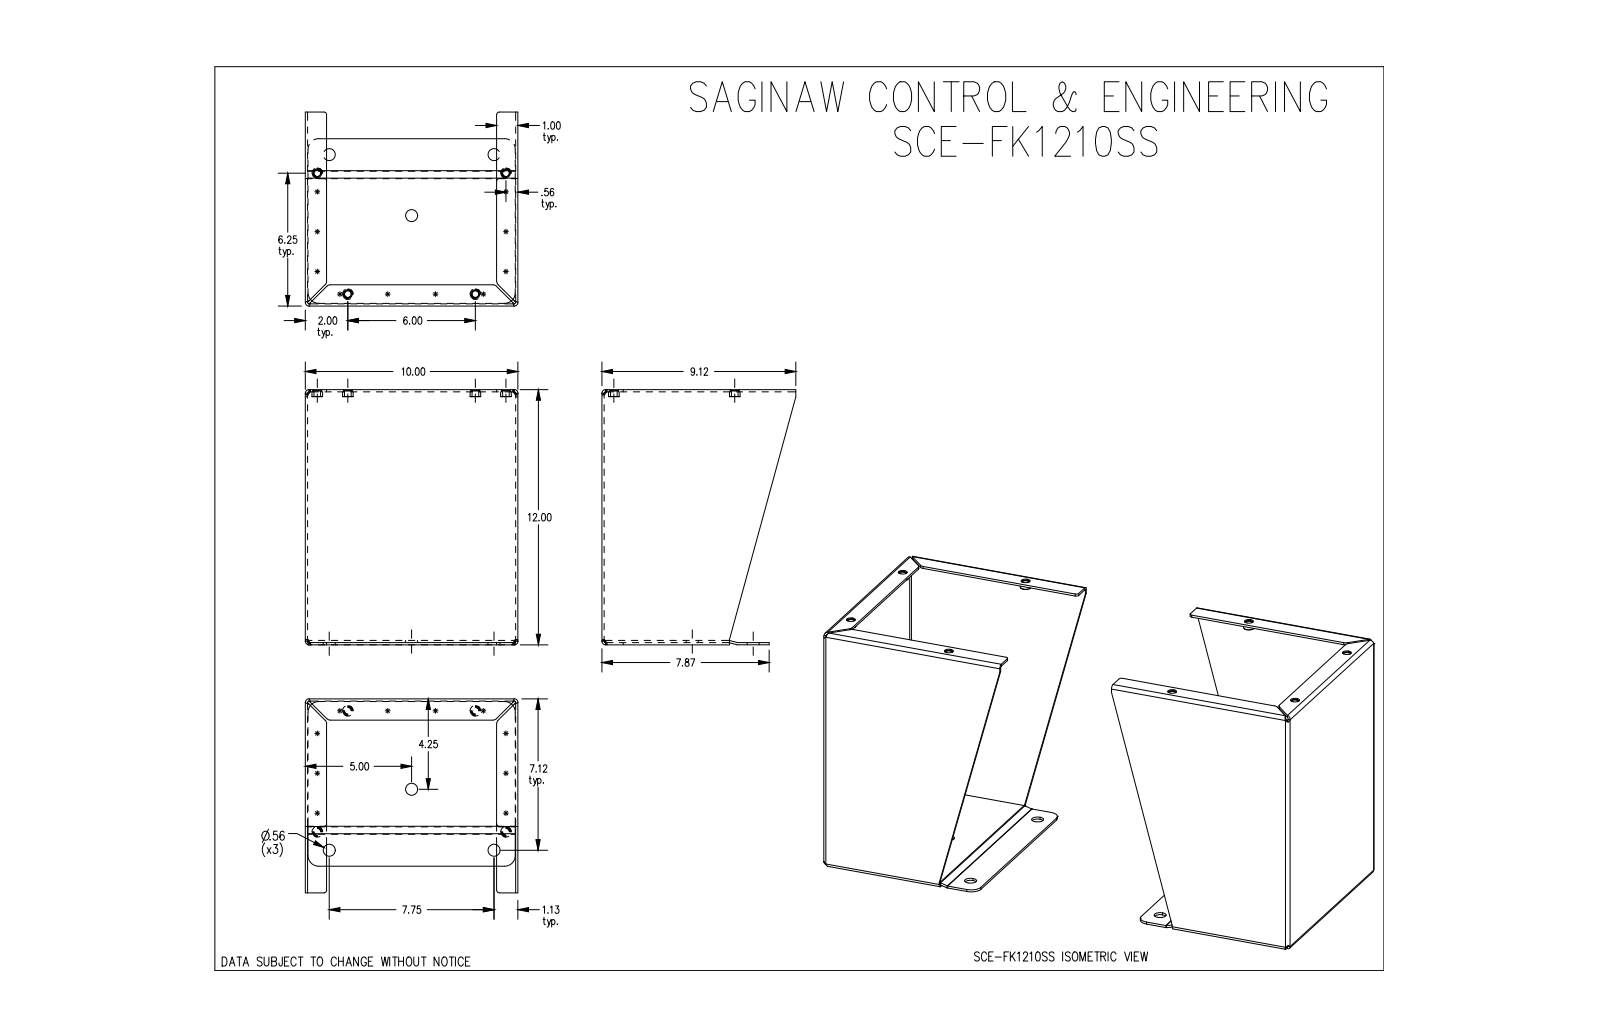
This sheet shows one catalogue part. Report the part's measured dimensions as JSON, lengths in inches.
{"part_name": "SCE-FK1210SS", "step_written_by": "SolidWorks 2019 (CONFIG_CONTROL_DESIGN)", "units": "inches", "bodies": {"solids": 12, "faces": 286, "planar": 120, "cylindrical": 110, "other": 56}, "overall_size": [24, 12, 10], "volume_in3": 85.55, "surface_area_in2": 1674, "round_holes": [[0.312, 8], [0.413, 8], [0.563, 6]], "round_bosses_or_shafts": [[0.5, 8], [0.412, 8]], "partial_cylinders_radius": [[0.166, 16], [0.063, 12], [0.125, 8], [0.22, 8], [0.5, 8], [0.062, 6]], "face_to_face_distances": [0.104, 9.896, 23.896, 9.792, 10, 23.792, 24, 11.792, 11.896, 0.101], "hole_center_spacings": [1.035, 4.755, 4.867, 5.866, 6.614, 9.363, 10.646, 13.211]}
